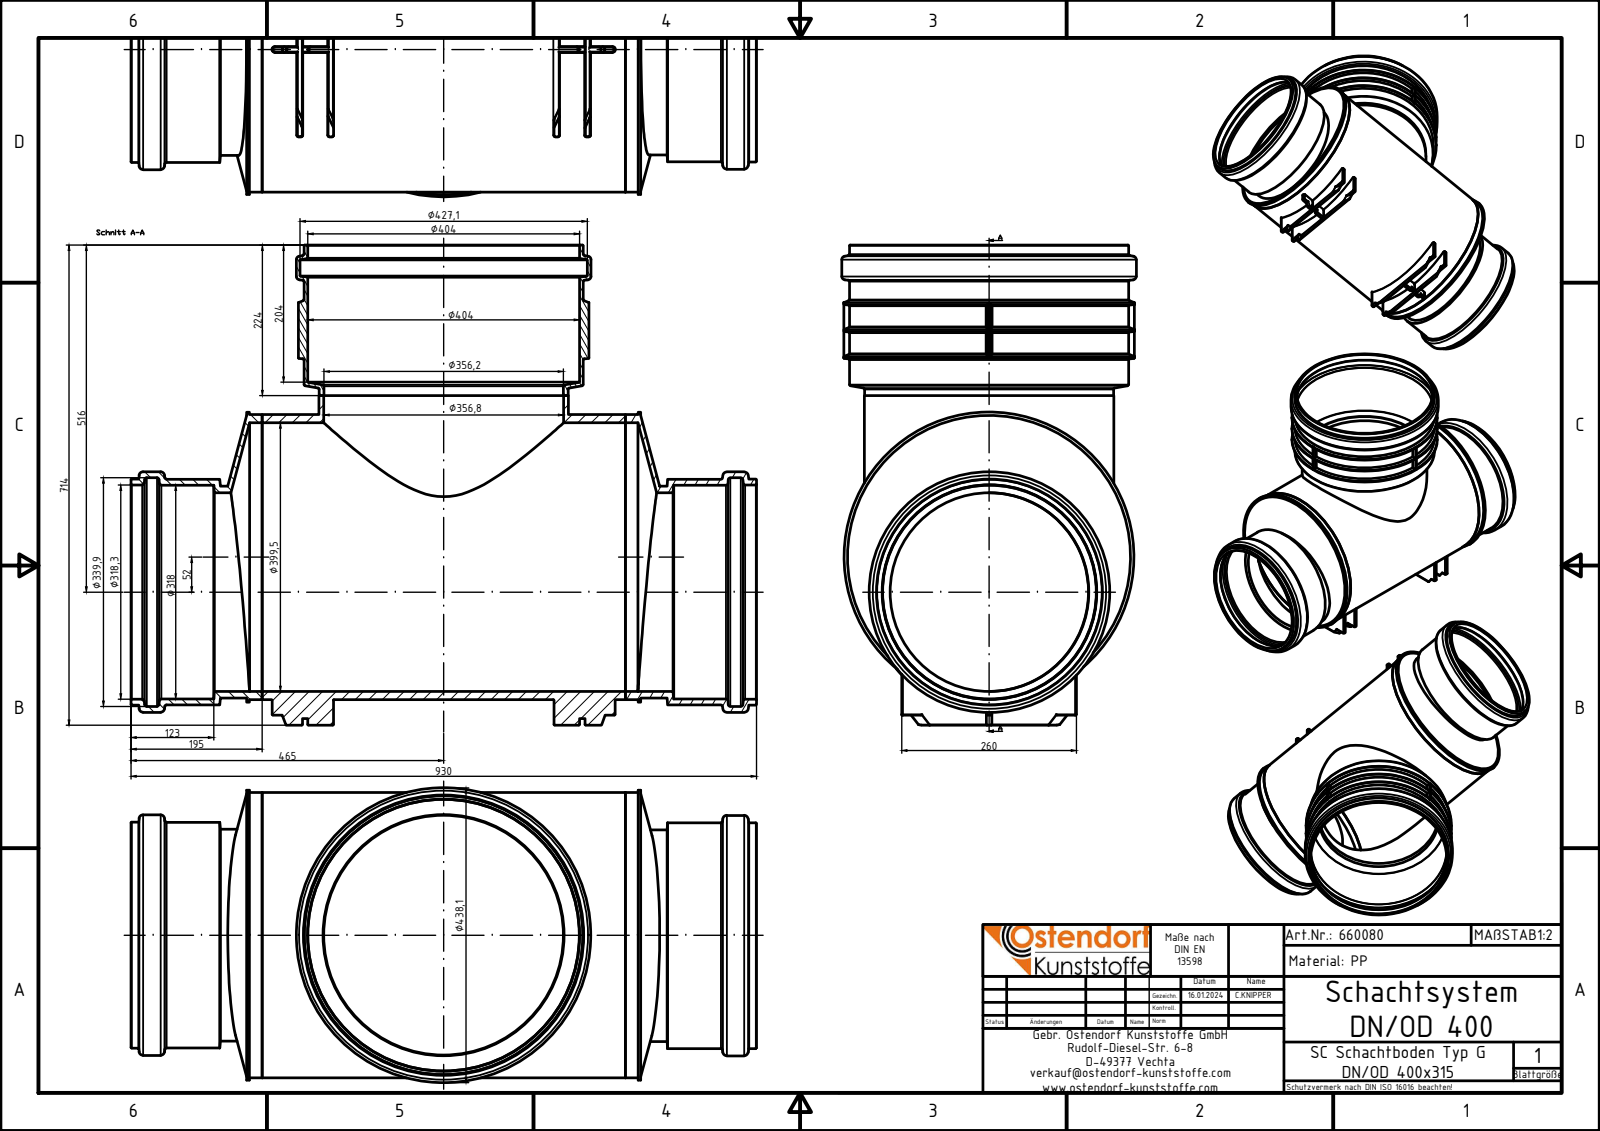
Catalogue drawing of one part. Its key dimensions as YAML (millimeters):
part_name: "660080z; 660080 Teil 2; 660080 Teil 3; 660080 Teil 1"
step_written_by: "Autodesk Inventor 2024 (AUTOMOTIVE_DESIGN)"
units: millimeters
bodies: {solids: 4, faces: 410, planar: 97, cylindrical: 145, other: 168}
overall_size: [930, 714, 438.1]
volume: 15380000
surface_area: 3425000
round_holes:
  - {diameter: 295.5, count: 2}
  - {diameter: 318, count: 2}
  - {diameter: 318.3, count: 2}
  - {diameter: 339.9, count: 2}
  - {diameter: 356.2, count: 1}
  - {diameter: 356.8, count: 1}
  - {diameter: 399.5, count: 1}
  - {diameter: 404, count: 1}
  - {diameter: 427.1, count: 1}
round_bosses_or_shafts:
  - {diameter: 357.5, count: 2}
  - {diameter: 335.9, count: 2}
  - {diameter: 335.6, count: 2}
  - {diameter: 314.9, count: 2}
  - {diameter: 438.1, count: 1}
  - {diameter: 432, count: 1}
  - {diameter: 431.1, count: 1}
  - {diameter: 424.1, count: 1}
partial_cylinders:
  - {radius: 1, count: 36}
  - {radius: 2, count: 24}
  - {radius: 4, count: 4}
face_to_face_distances: [8, 46, 382, 540, 434, 106, 480, 60, 374, 52]
hole_center_spacings: [52, 0.76]
